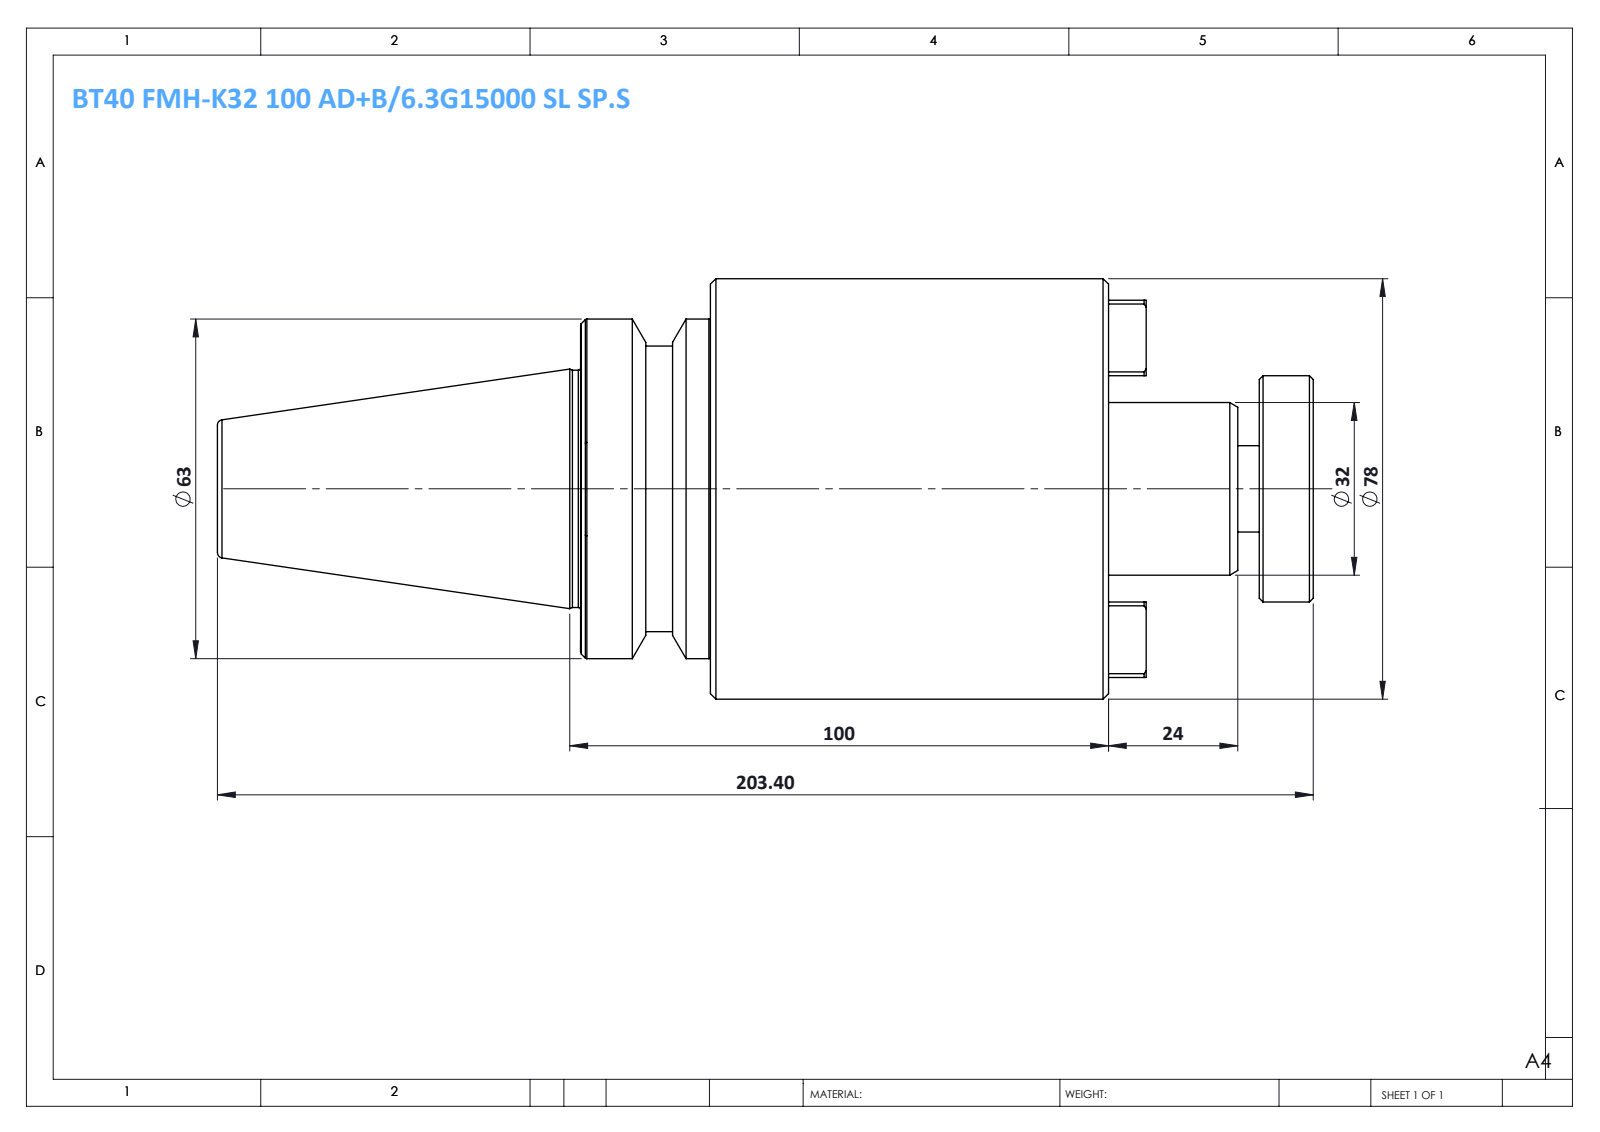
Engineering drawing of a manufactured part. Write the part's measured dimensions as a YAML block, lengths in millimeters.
part_name: "BT40 FMH32 100 AD-6.3G15000 SL SP"
step_written_by: "SolidWorks 2014 (CONFIG_CONTROL_DESIGN)"
units: millimeters
bodies: {solids: 1, faces: 87, planar: 35, cylindrical: 16, other: 36}
overall_size: [203.4, 78, 78]
volume: 525046
surface_area: 46328
round_bosses_or_shafts:
  - {diameter: 78, count: 1}
  - {diameter: 63, count: 1}
  - {diameter: 53, count: 1}
  - {diameter: 44, count: 1}
  - {diameter: 42, count: 1}
  - {diameter: 32, count: 1}
  - {diameter: 16, count: 1}
face_to_face_distances: [73.88, 98, 24.12, 38, 111.88, 136, 28, 10, 101.88, 126]
